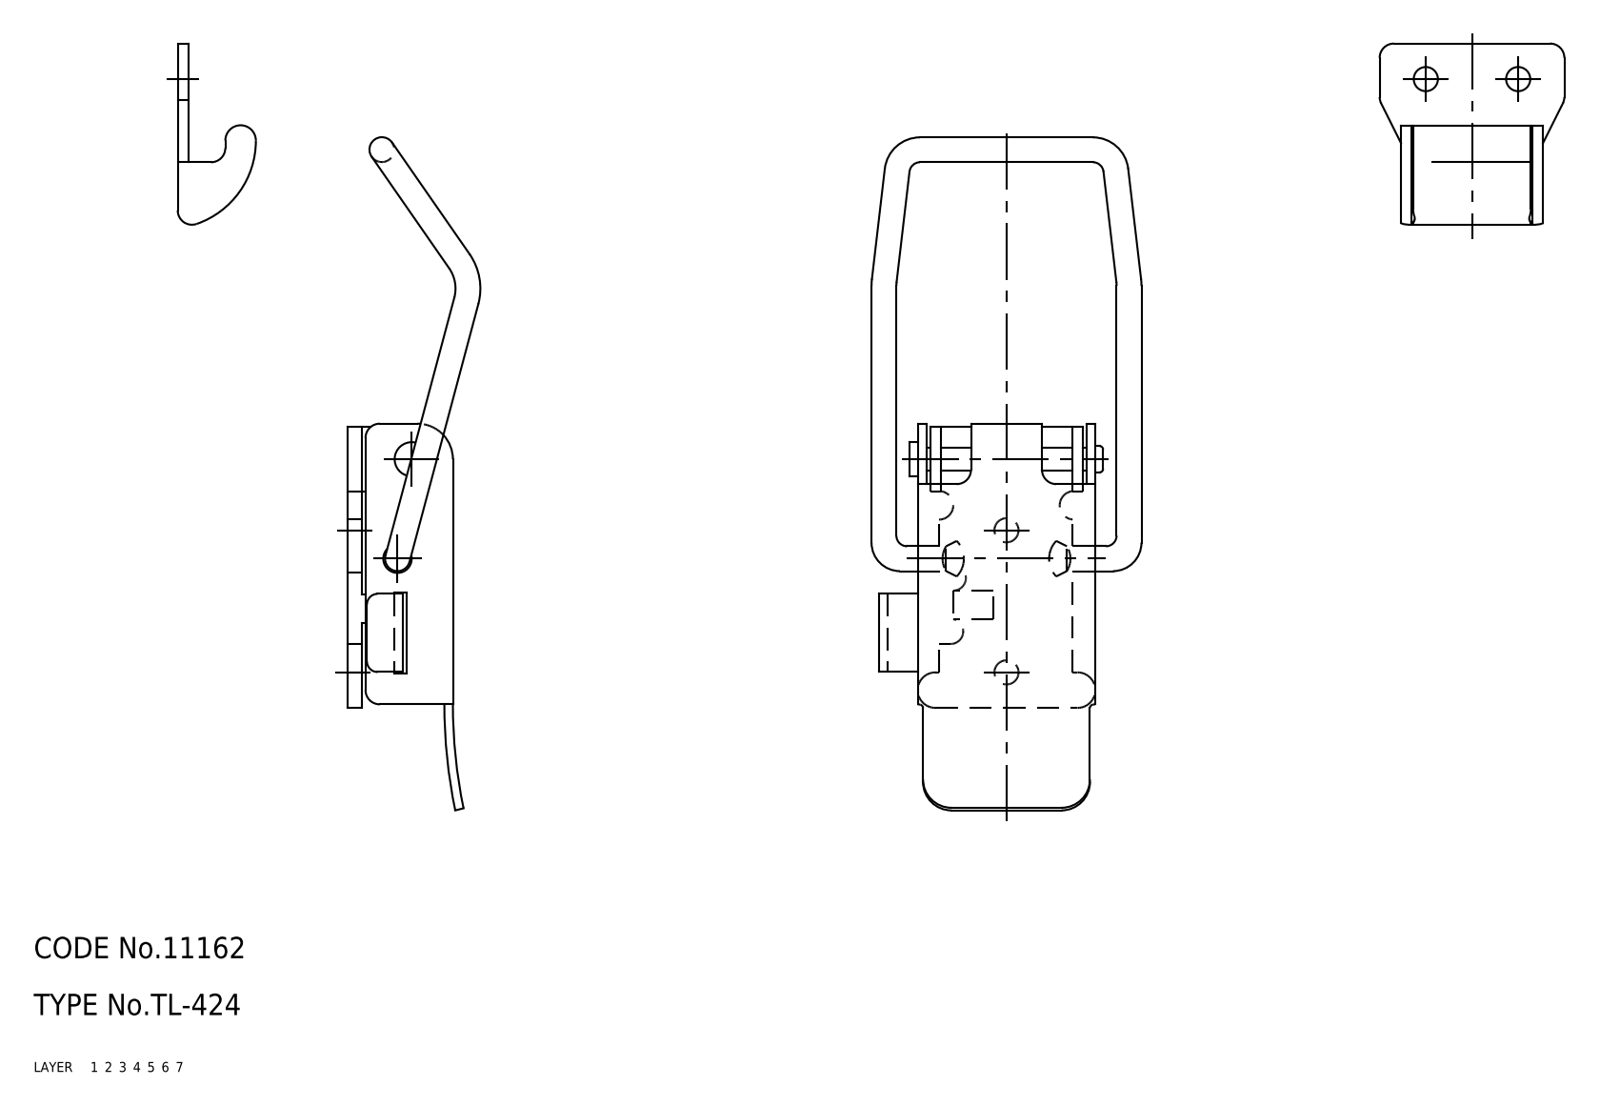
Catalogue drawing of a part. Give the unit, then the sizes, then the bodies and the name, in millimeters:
Units: millimetres
Overall size (bounding box): 124.43 × 38 × 18.67
Round holes (diameter × count): ⌀3.4 ×5, ⌀4 ×1
Round bosses / shafts (diameter × count): ⌀3.5 ×6, ⌀4.8 ×1, ⌀3.7 ×1, ⌀3.3 ×1
Partial cylindrical surfaces — rounded edges, fillets, slot ends (radius × count): R2 ×12, R1 ×10, R0.5 ×9, R0.4 ×2, R1.5 ×2, R2.01 ×2, R2.5 ×2, R3 ×2
Main face-to-face distances: 1.2, 1.5, 2, 23.8, 14.8, 12.8, 11.6, 13.6, 12.89, 11.69
Hole centre spacings: 80.26, 100.21, 13, 14.14, 20
Volume: 8 002 mm³ · Surface area: 12 128 mm²
Bodies: 3 solids, 370 faces (125 planar, 120 cylindrical, 125 other)
Part name (STEP PRODUCT): キーパー変更; レバー; アーム_M7; TL_424
STEP written by: SolidWorks 2015 (AUTOMOTIVE_DESIGN)
